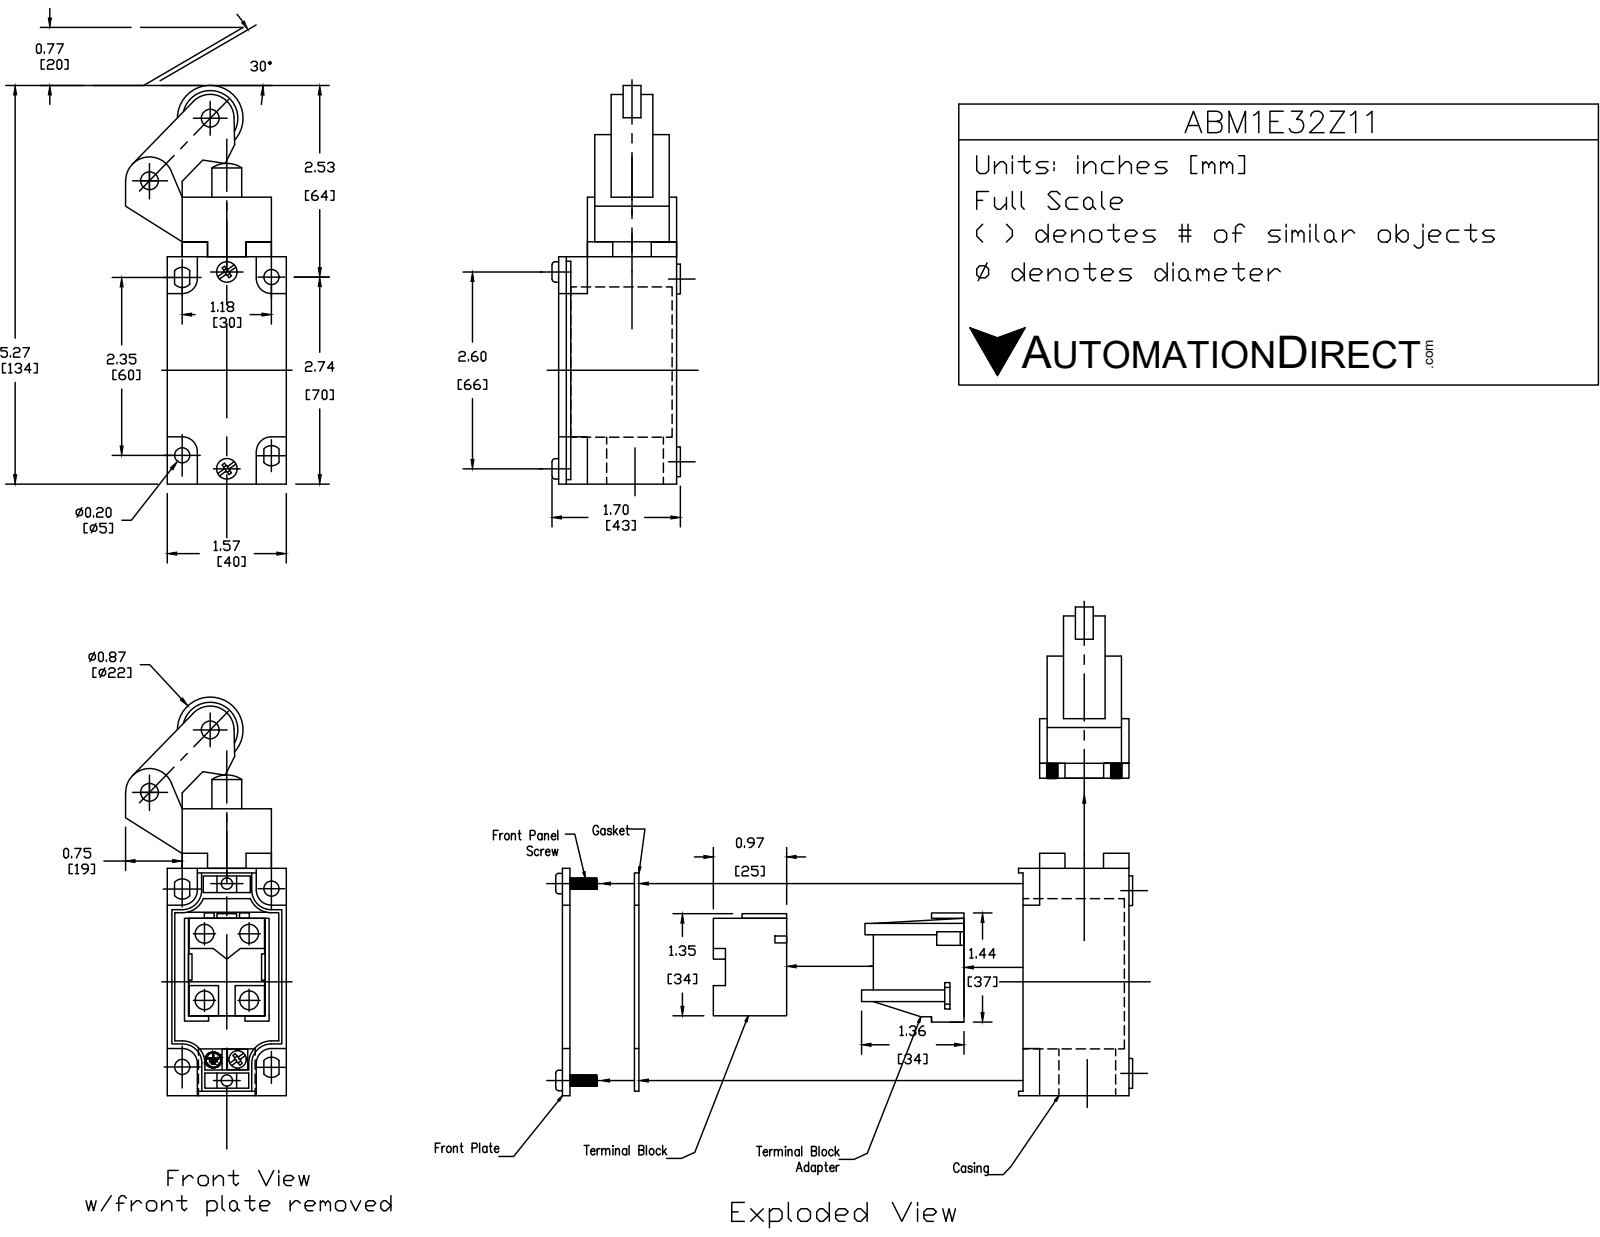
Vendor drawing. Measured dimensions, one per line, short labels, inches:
name: ABM1E32Z11
written by: SolidWorks 2017 (AUTOMOTIVE_DESIGN)
unit: in
bodies: 4 solids, 221 faces (108 planar, 90 cylindrical, 23 other)
size: 5.287 × 2.126 × 1.705
volume: 8.579 in³; area: 50.73 in²
holes: 2× ⌀0.205, 1× ⌀0.394, 1× ⌀0.669, 1× ⌀0.748
bosses: 5× ⌀0.394, 3× ⌀0.276, 1× ⌀0.866, 1× ⌀0.453
rounds: 16× R0.059, 5× R0.039, 4× R0.197, 2× R0.128, 2× R0.315, 2× R0.472, 1× R0.236, 1× R0.453
face distances: 1.575, 0.325, 1.555, 0.118, 0.197, 0.738, 1.181, 0.856, 0.443, 0.413
hole spacings: 0.039, 2.641
